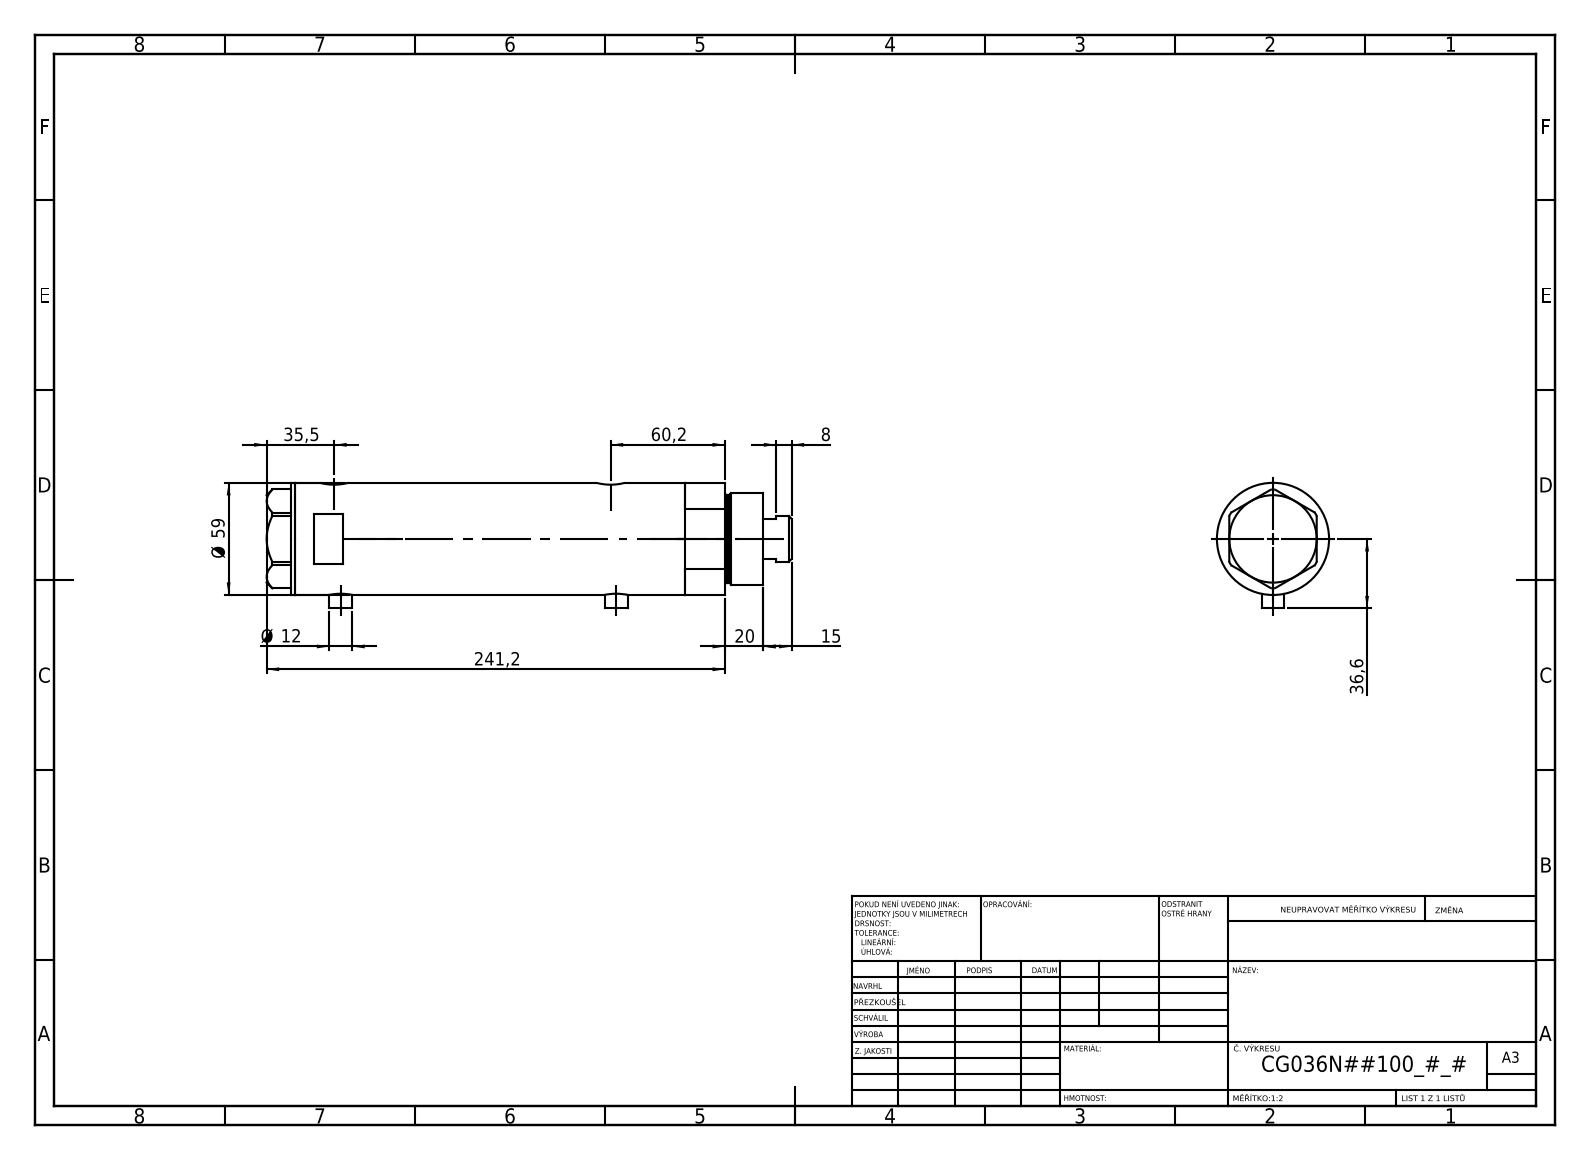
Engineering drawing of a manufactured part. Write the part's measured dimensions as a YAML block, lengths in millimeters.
part_name: "V270CG_MIDDLE; V270CG_VC; V270CG_BACK; V270CG_FRONT"
step_written_by: "SolidWorks 2019 (CONFIG_CONTROL_DESIGN)"
units: millimeters
bodies: {solids: 4, faces: 120, planar: 51, cylindrical: 49, other: 20}
overall_size: [276.2, 66.1, 59]
volume: 629802
surface_area: 124998
round_holes:
  - {diameter: 9.73, count: 2}
  - {diameter: 12.5, count: 2}
  - {diameter: 15, count: 2}
  - {diameter: 8.5, count: 1}
  - {diameter: 25, count: 1}
  - {diameter: 26.5, count: 1}
  - {diameter: 36, count: 1}
  - {diameter: 40, count: 1}
  - {diameter: 52, count: 1}
round_bosses_or_shafts:
  - {diameter: 12, count: 2}
  - {diameter: 59, count: 1}
  - {diameter: 48, count: 1}
  - {diameter: 46, count: 1}
  - {diameter: 24, count: 1}
face_to_face_distances: [167.2, 23.5, 143.7, 15, 38.5, 182.2, 2, 261.2, 246.2, 222.7]
hole_center_spacings: [2.9, 3.5, 142, 144.9, 145.5, 148.4]
